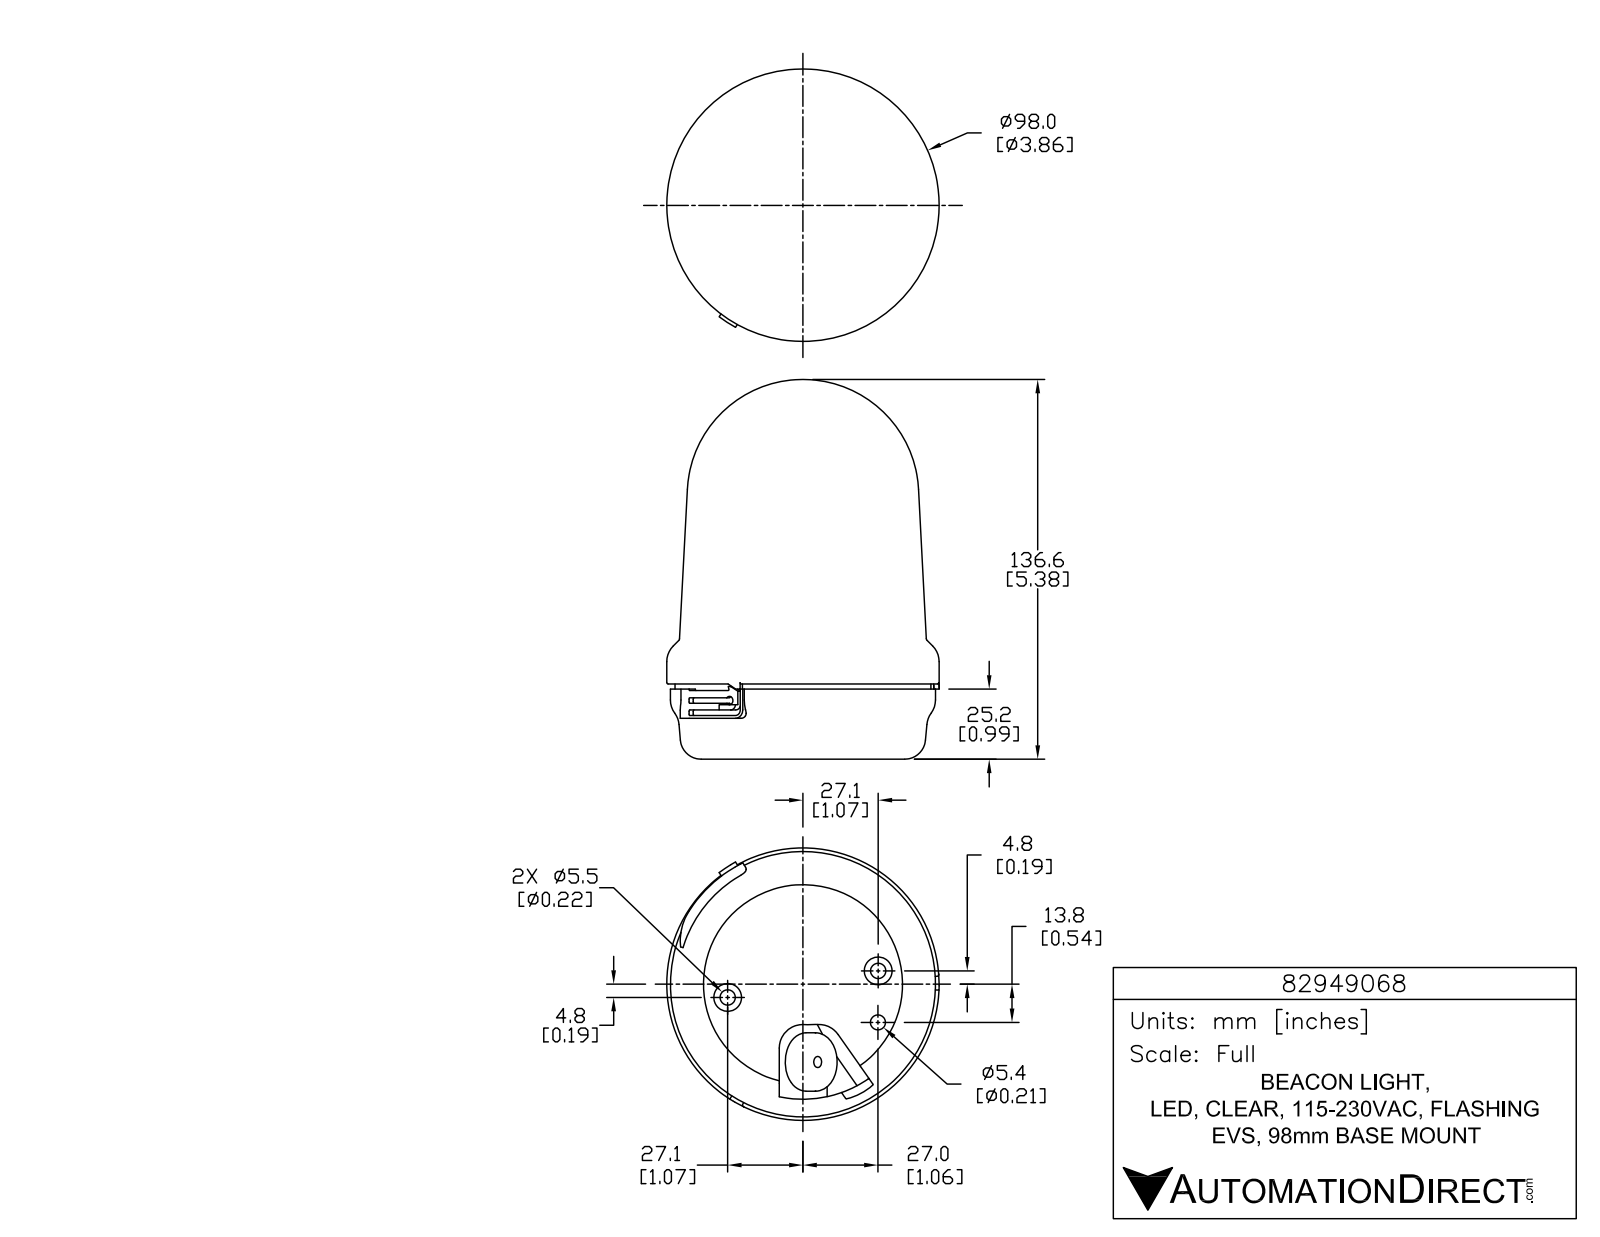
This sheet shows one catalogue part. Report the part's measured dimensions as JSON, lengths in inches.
{"part_name": "82949068", "step_written_by": "SolidWorks 2015 (AUTOMOTIVE_DESIGN)", "units": "inches", "bodies": {"solids": 1, "faces": 872, "planar": 566, "cylindrical": 204, "other": 102}, "overall_size": [5.378, 3.858, 3.858], "volume_in3": 44.69, "surface_area_in2": 73.66, "round_holes": [[0.059, 3], [0.217, 2], [0.157, 1], [0.213, 1], [2.819, 1]], "round_bosses_or_shafts": [[0.339, 3], [0.084, 3], [0.394, 2], [3.858, 1], [3.756, 1], [3.626, 1], [0.827, 1]], "partial_cylinders_radius": [[0.005, 9], [0.005, 6], [0.012, 6], [0.012, 6], [0.012, 6], [0.196, 6], [0.02, 5], [0.039, 4]], "face_to_face_distances": [1.045, 0.972, 0.073, 0.02, 0.992, 1.065, 0.236, 0.579, 0.559, 0.413], "hole_center_spacings": [1.083, 0.73, 1.193, 2.158, 2.165]}
